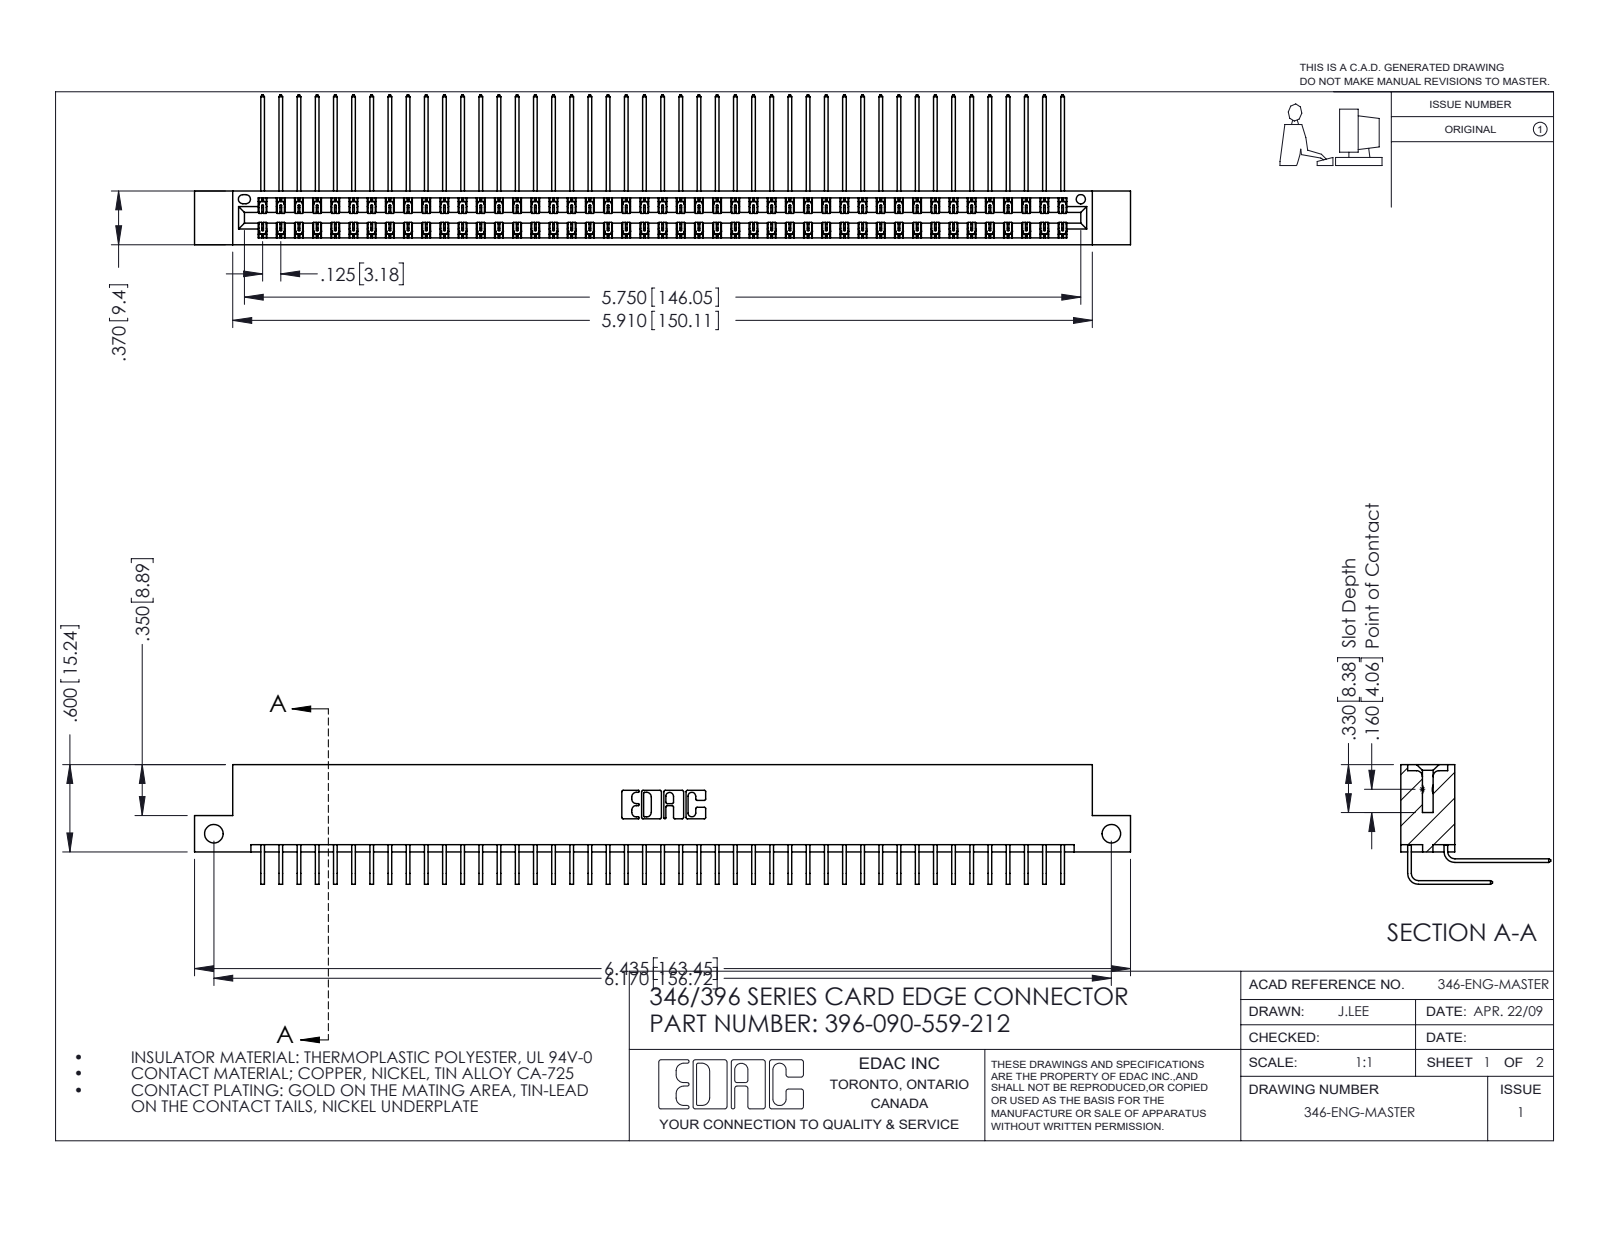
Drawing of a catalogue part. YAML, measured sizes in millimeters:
part_name: "396-090-559-212; 345-292-001_559 Tail - 2; 345-292-001_558 559 Tail - 1; 346 Part_Flush Mounting Lugs - Side Mount"
step_written_by: "SolidWorks 2016 (CONFIG_CONTROL_DESIGN)"
units: millimeters
bodies: {solids: 91, faces: 4982, planar: 3406, cylindrical: 1576, other: 0}
overall_size: [163.4, 26.2, 20.9]
volume: 16390
surface_area: 24940
round_holes:
  - {diameter: 3.3, count: 2}
  - {diameter: 1.6, count: 1}
partial_cylinders:
  - {radius: 0.2, count: 135}
  - {radius: 0.3, count: 22}
  - {radius: 0.2, count: 6}
  - {radius: 0.8, count: 6}
  - {radius: 0.7, count: 3}
  - {radius: 0.4, count: 2}
  - {radius: 0.6, count: 2}
  - {radius: 0.6, count: 2}
face_to_face_distances: [1.2, 8.2, 0.6, 9.4, 6.4, 1.8, 7.6, 7, 3.8, 5.6]
hole_center_spacings: [156.7]
